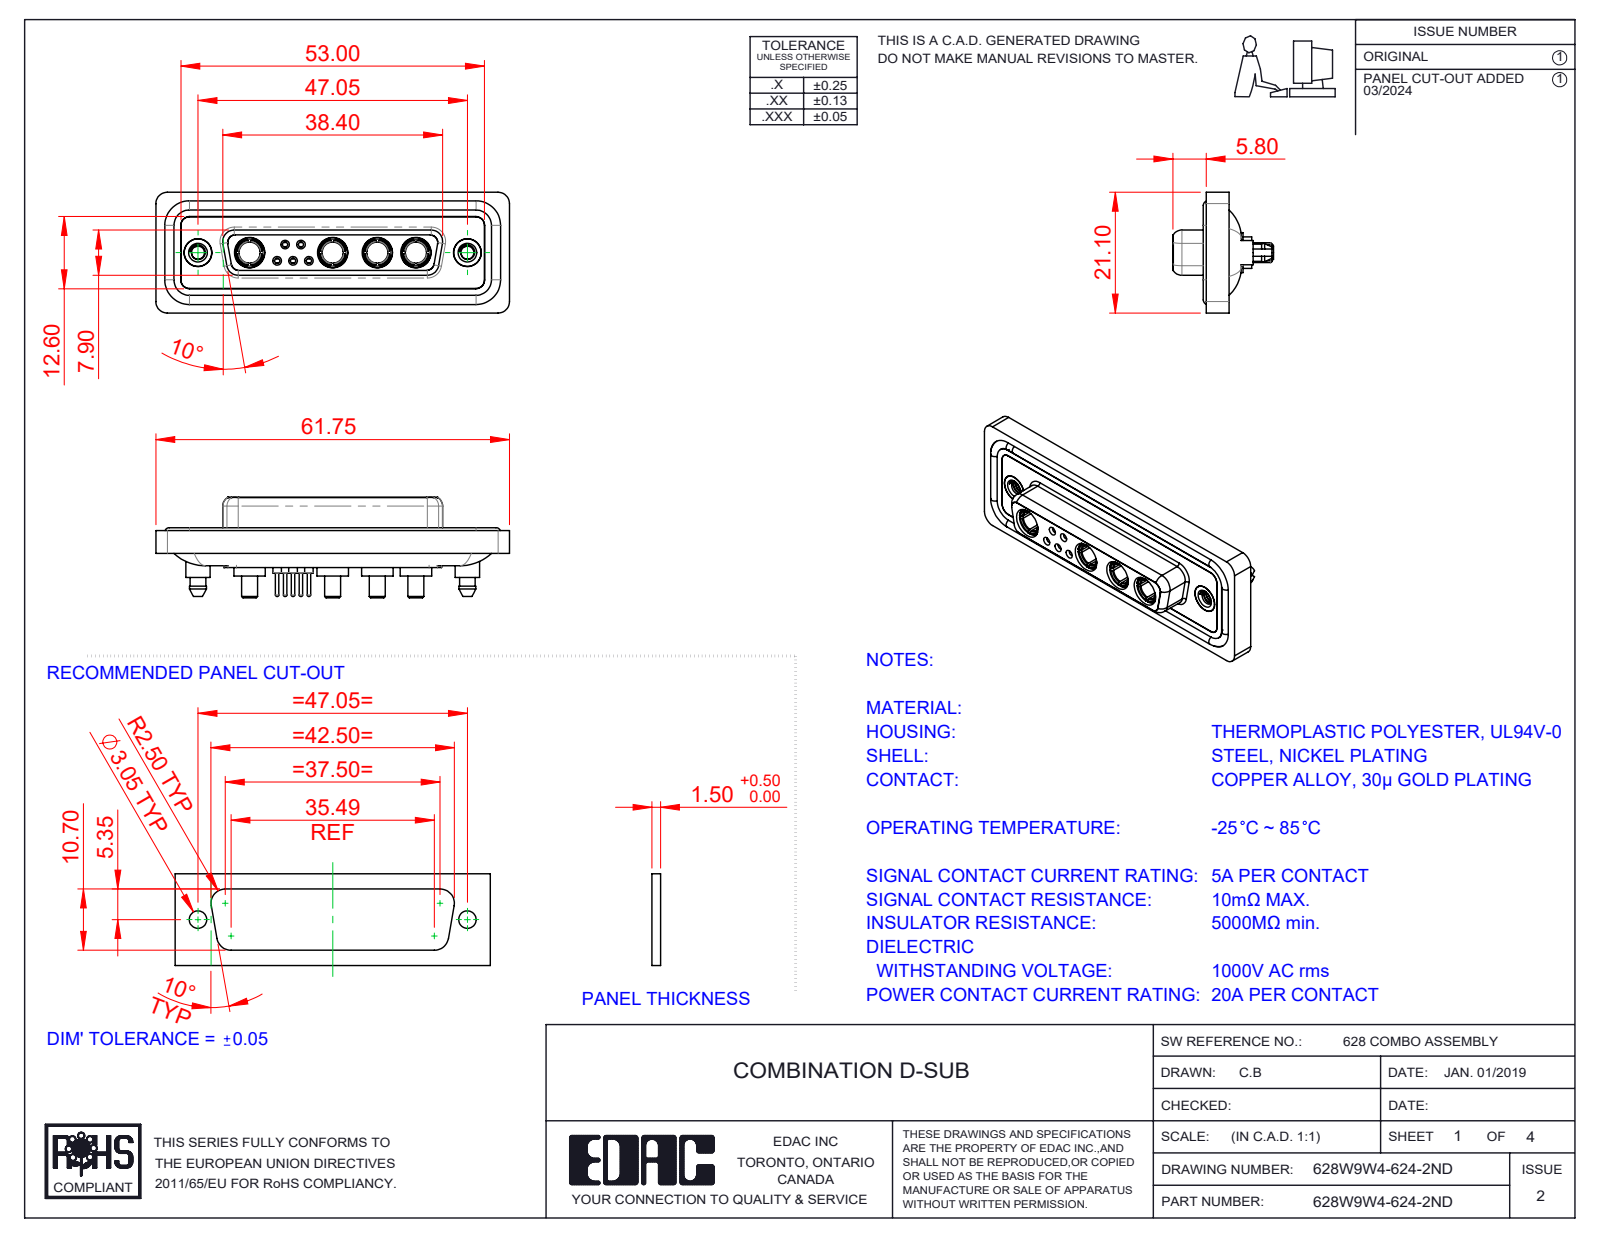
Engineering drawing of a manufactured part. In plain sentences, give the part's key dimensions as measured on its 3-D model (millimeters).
The part is named "628Combo Waterproof Housing_25 Contacts; 628Combo Threaded Boardlock_D; 628W9W4-624-2ND; Power Socket_20A S (+5 more)". Its 3-D file was written by "SolidWorks 2023 (CONFIG_CONTROL_DESIGN)". It is 20 solids with 1023 faces: 312 planar, 423 cylindrical and 288 other. Overall it measures 61.75 by 21.1 by 17.55 millimeters. Its volume is 8 359 cubic millimeters and its surface area 13 901 square millimeters. Round holes: 6 of diameter 4.85, 5 of diameter 0.9, 5 of diameter 1.1, 5 of diameter 1.5, 5 of diameter 2, 4 of diameter 3.7, 4 of diameter 5.3, 3 of diameter 1.6, 2 of diameter 1.7, 2 of diameter 2.26, 2 of diameter 4, 2 of diameter 4.05. Round bosses or shafts: 6 of diameter 1.6, 5 of diameter 2.2, 5 of diameter 0.6, 4 of diameter 5.5, 4 of diameter 5.2, 4 of diameter 4.96, 4 of diameter 4.75, 4 of diameter 3.75. Partial cylindrical surfaces (rounded edges, fillets, slot ends): 24 of radius 1.5, 18 of radius 2, 10 of radius 1.6, 8 of radius 1.35, 4 of radius 0.25, 4 of radius 0.5, 4 of radius 0.6, 4 of radius 0.65. The main face-to-face distances are 0.4, 1.8, 7.45, 5.65, 0.5, 7.05, 6.6, 1.6, 1.1, 2.9. The hole center spacings are 3.16, 2.77, 5.03, 2.76, 4.4, 5.02, 5.54, 5.73.
